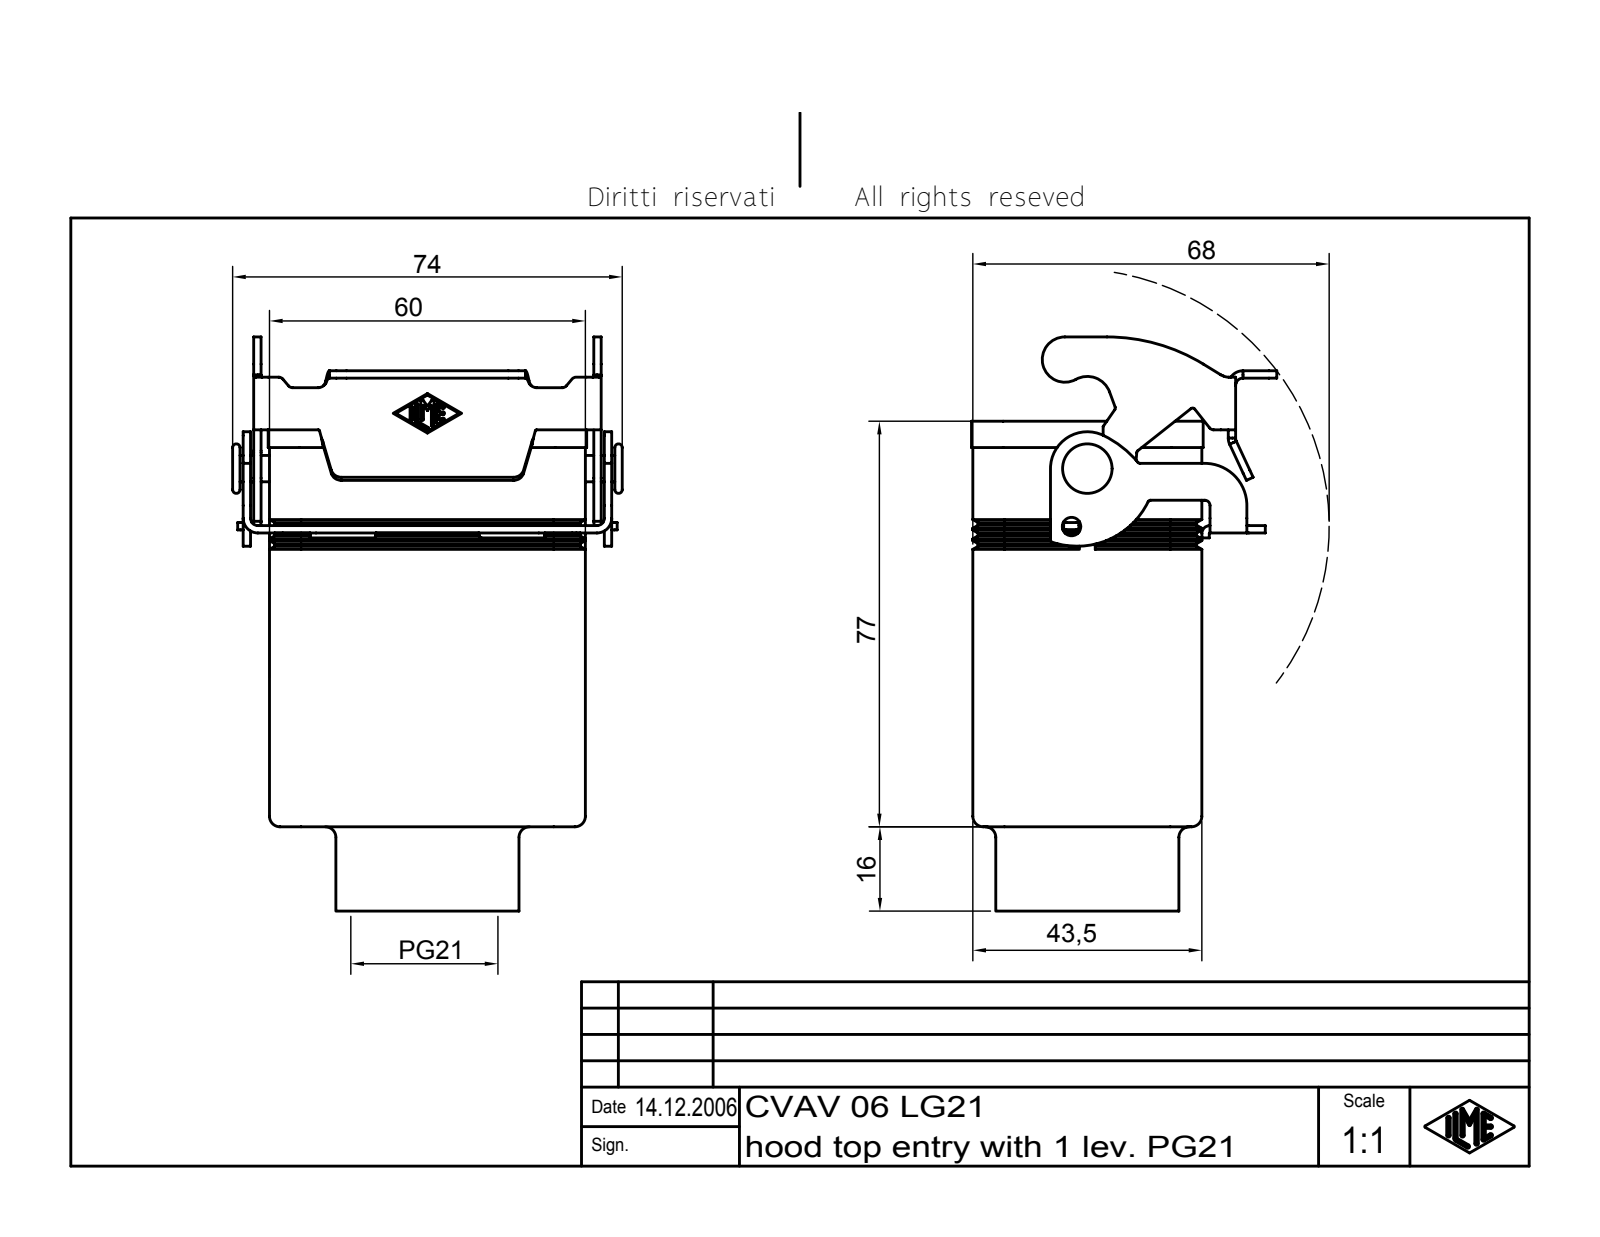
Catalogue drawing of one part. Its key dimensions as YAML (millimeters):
part_name: "CVAV 06 LG21"
step_written_by: "Autodesk Inventor 7 (AUTOMOTIVE_DESIGN)"
units: millimeters
bodies: {solids: 2, faces: 494, planar: 155, cylindrical: 127, other: 212}
overall_size: [109, 74, 57.98]
volume: 77964
surface_area: 46838
round_holes:
  - {diameter: 3.5, count: 1}
  - {diameter: 23.78, count: 1}
  - {diameter: 26.78, count: 1}
round_bosses_or_shafts:
  - {diameter: 34.78, count: 1}
  - {diameter: 5, count: 1}
  - {diameter: 3.2, count: 1}
partial_cylinders:
  - {radius: 0.25, count: 15}
  - {radius: 2, count: 10}
  - {radius: 0.5, count: 9}
  - {radius: 1.5, count: 9}
  - {radius: 1, count: 8}
  - {radius: 6, count: 8}
  - {radius: 1.4, count: 6}
  - {radius: 2.8, count: 6}
face_to_face_distances: [3, 40.5, 43.5, 57, 37.5, 60, 11.75, 8.75, 11.5, 48.5]
